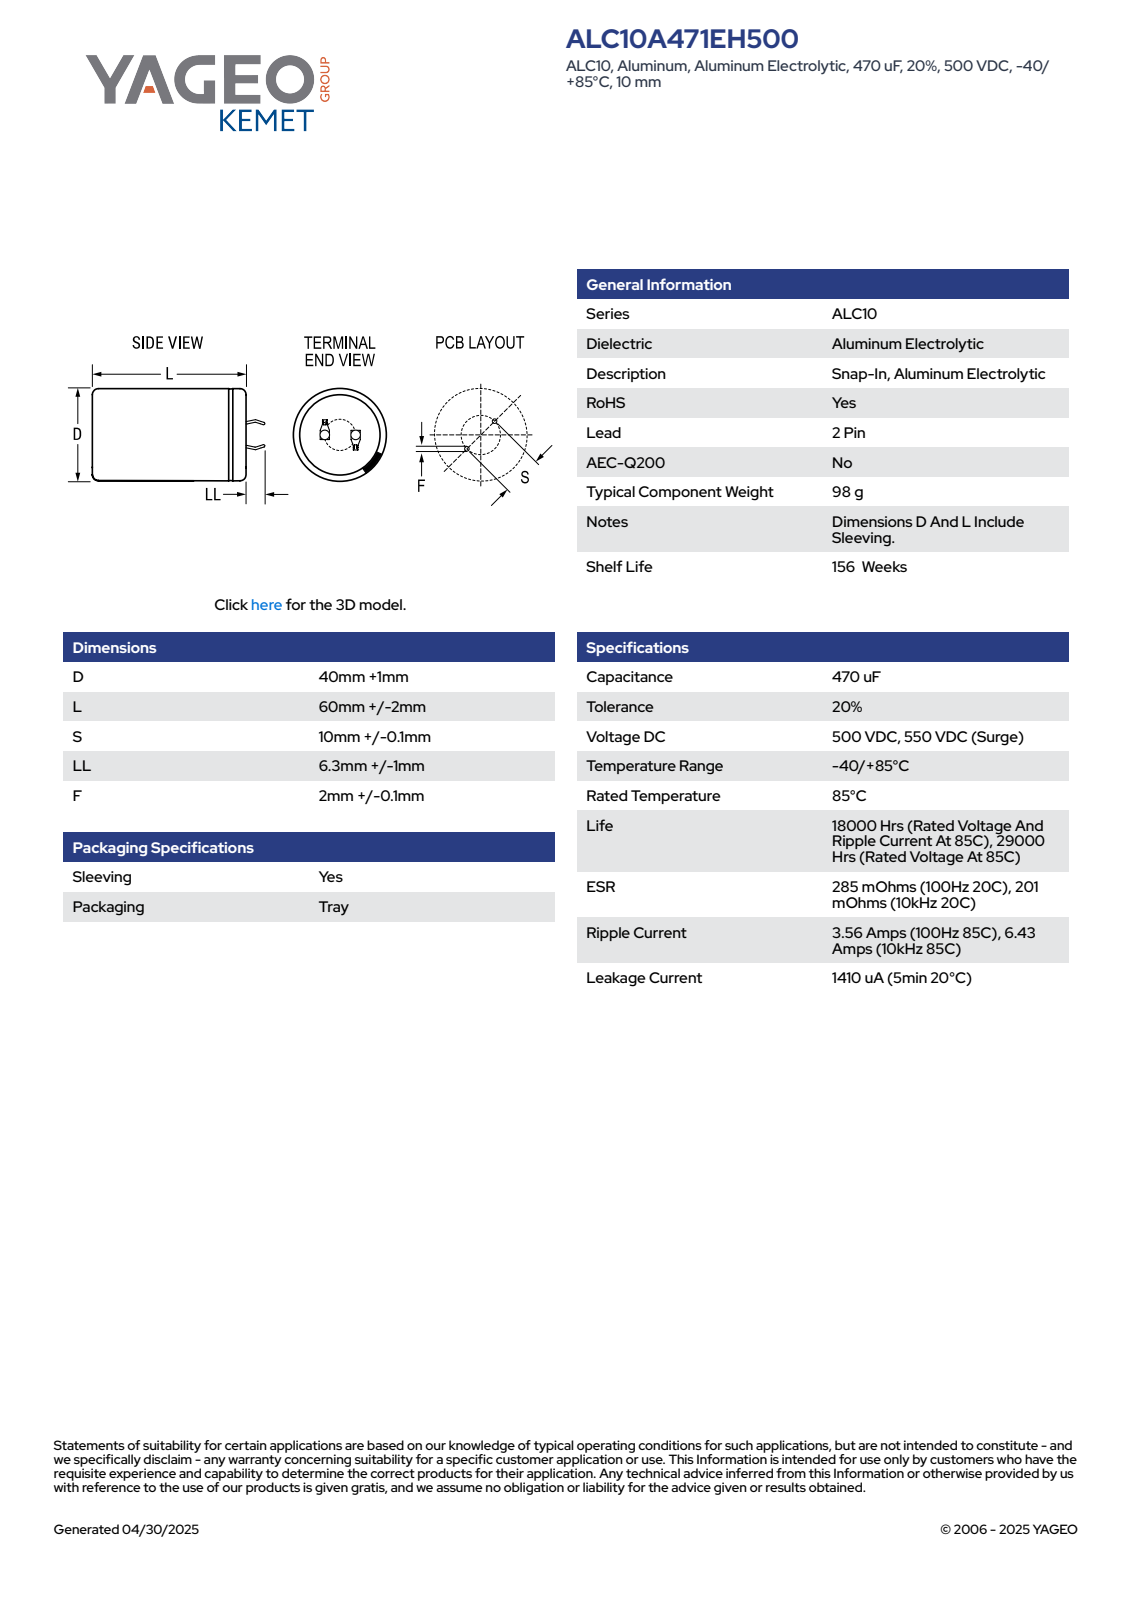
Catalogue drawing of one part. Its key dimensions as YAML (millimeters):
part_name: "CARS_K2P_40X60_D41L62S10LL7.3F2.1"
step_written_by: "SolidWorks 2014 (AUTOMOTIVE_DESIGN)"
units: millimeters
bodies: {solids: 1, faces: 100, planar: 52, cylindrical: 9, other: 39}
overall_size: [69.29, 41, 41]
volume: 81071
surface_area: 10609
round_holes:
  - {diameter: 36.28, count: 1}
round_bosses_or_shafts:
  - {diameter: 41, count: 1}
partial_cylinders:
  - {radius: 20.49, count: 1}
face_to_face_distances: [61.99, 0.6, 62.49, 0.5, 7.08, 7.64, 0.75, 1.35, 7.68, 6.48]
